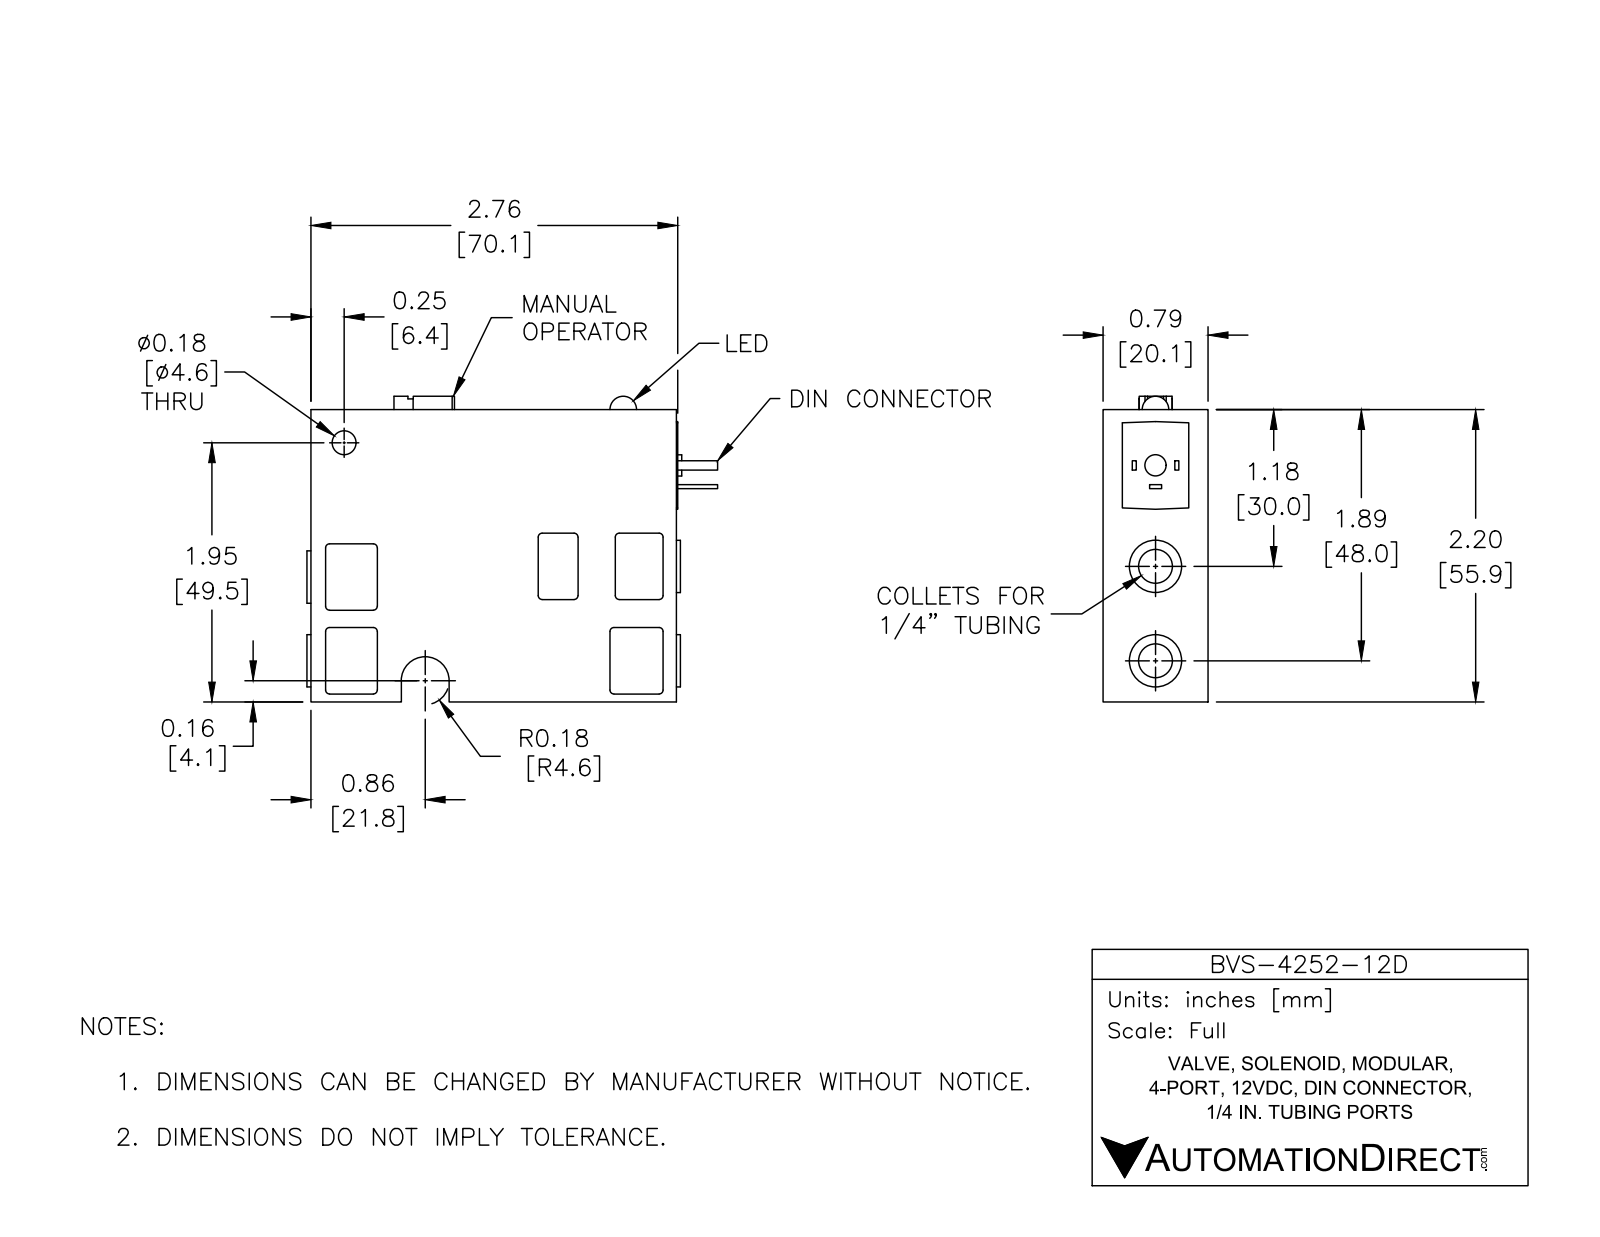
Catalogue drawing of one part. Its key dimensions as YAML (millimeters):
part_name: "BVS-4252-12D"
step_written_by: "SolidWorks 2016 (AUTOMOTIVE_DESIGN)"
units: millimeters
bodies: {solids: 1, faces: 169, planar: 99, cylindrical: 68, other: 2}
overall_size: [78.5, 58.4, 20.1]
volume: 71680
surface_area: 16250
round_holes:
  - {diameter: 6.5, count: 3}
  - {diameter: 2.5, count: 1}
  - {diameter: 4.6, count: 1}
round_bosses_or_shafts:
  - {diameter: 10, count: 3}
  - {diameter: 4.1, count: 1}
partial_cylinders:
  - {radius: 0.8, count: 20}
  - {radius: 0.5, count: 2}
  - {radius: 3.2, count: 1}
  - {radius: 4.6, count: 1}
face_to_face_distances: [20.1, 2.5, 55.9, 17.5, 69.9, 15, 12.7, 2.8, 67.3, 0.8]
hole_center_spacings: [2, 14, 16, 16, 18, 32]
